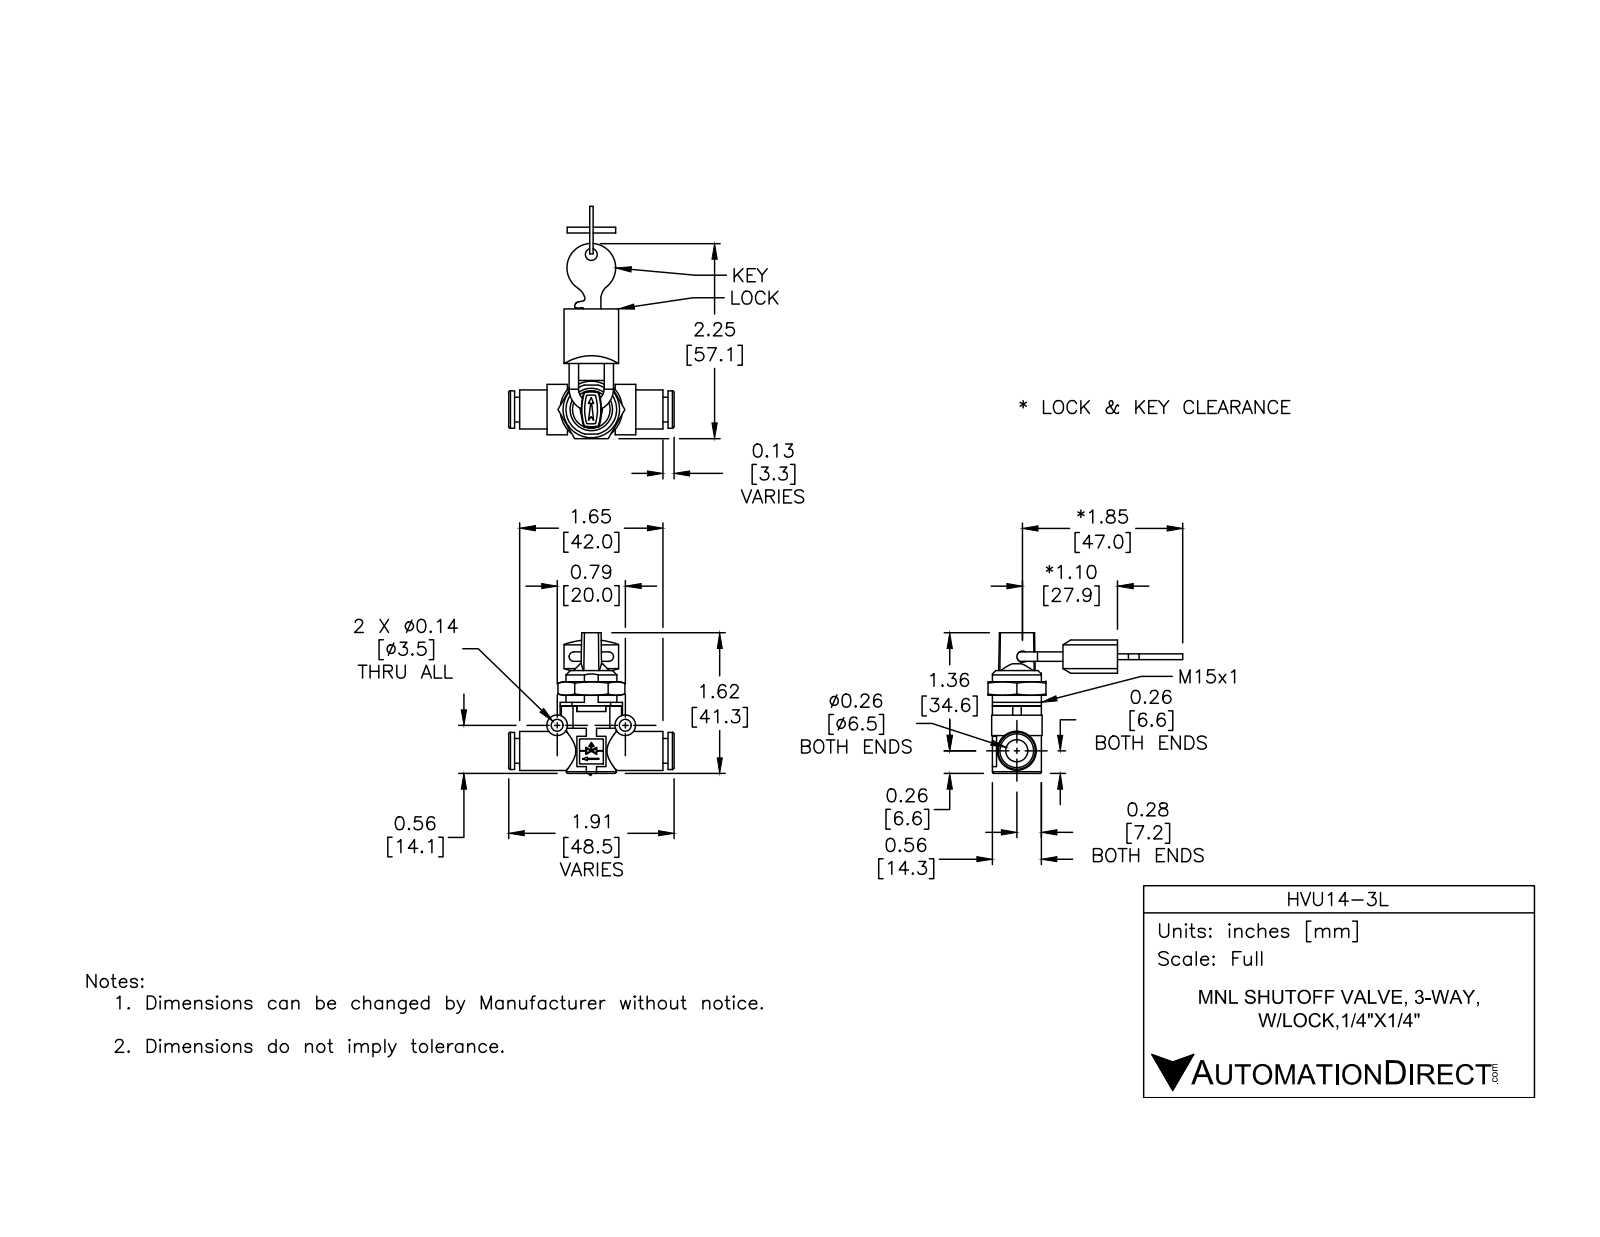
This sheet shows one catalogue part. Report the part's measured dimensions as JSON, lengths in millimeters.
{"part_name": "HVU14-3L", "step_written_by": "SolidWorks 2015 (CONFIG_CONTROL_DESIGN)", "units": "millimeters", "bodies": {"solids": 12, "faces": 253, "planar": 146, "cylindrical": 81, "other": 26}, "overall_size": [68.11, 48.5, 41.88], "volume_mm3": 12227, "surface_area_mm2": 10782, "round_holes": [[3.5, 4], [8, 2], [3.25, 1], [6.5, 1], [11, 1], [13.47, 1]], "round_bosses_or_shafts": [[14.25, 2], [6, 2], [2.75, 2], [14.9, 1], [14.65, 1], [14, 1], [11.45, 1], [10.9, 1]], "partial_cylinders_radius": [[0.5, 2], [2.5, 2], [4.05, 2], [5.58, 2], [7.03, 2], [14.56, 2], [24.18, 2], [9.12, 1]], "face_to_face_distances": [1.75, 1.7, 15.26, 16.96, 13.51, 15.21, 16, 2.6, 0.85, 12.66], "hole_center_spacings": [16.37, 22.48, 7.17, 20, 27.68, 45.44, 50.98, 59.42]}
